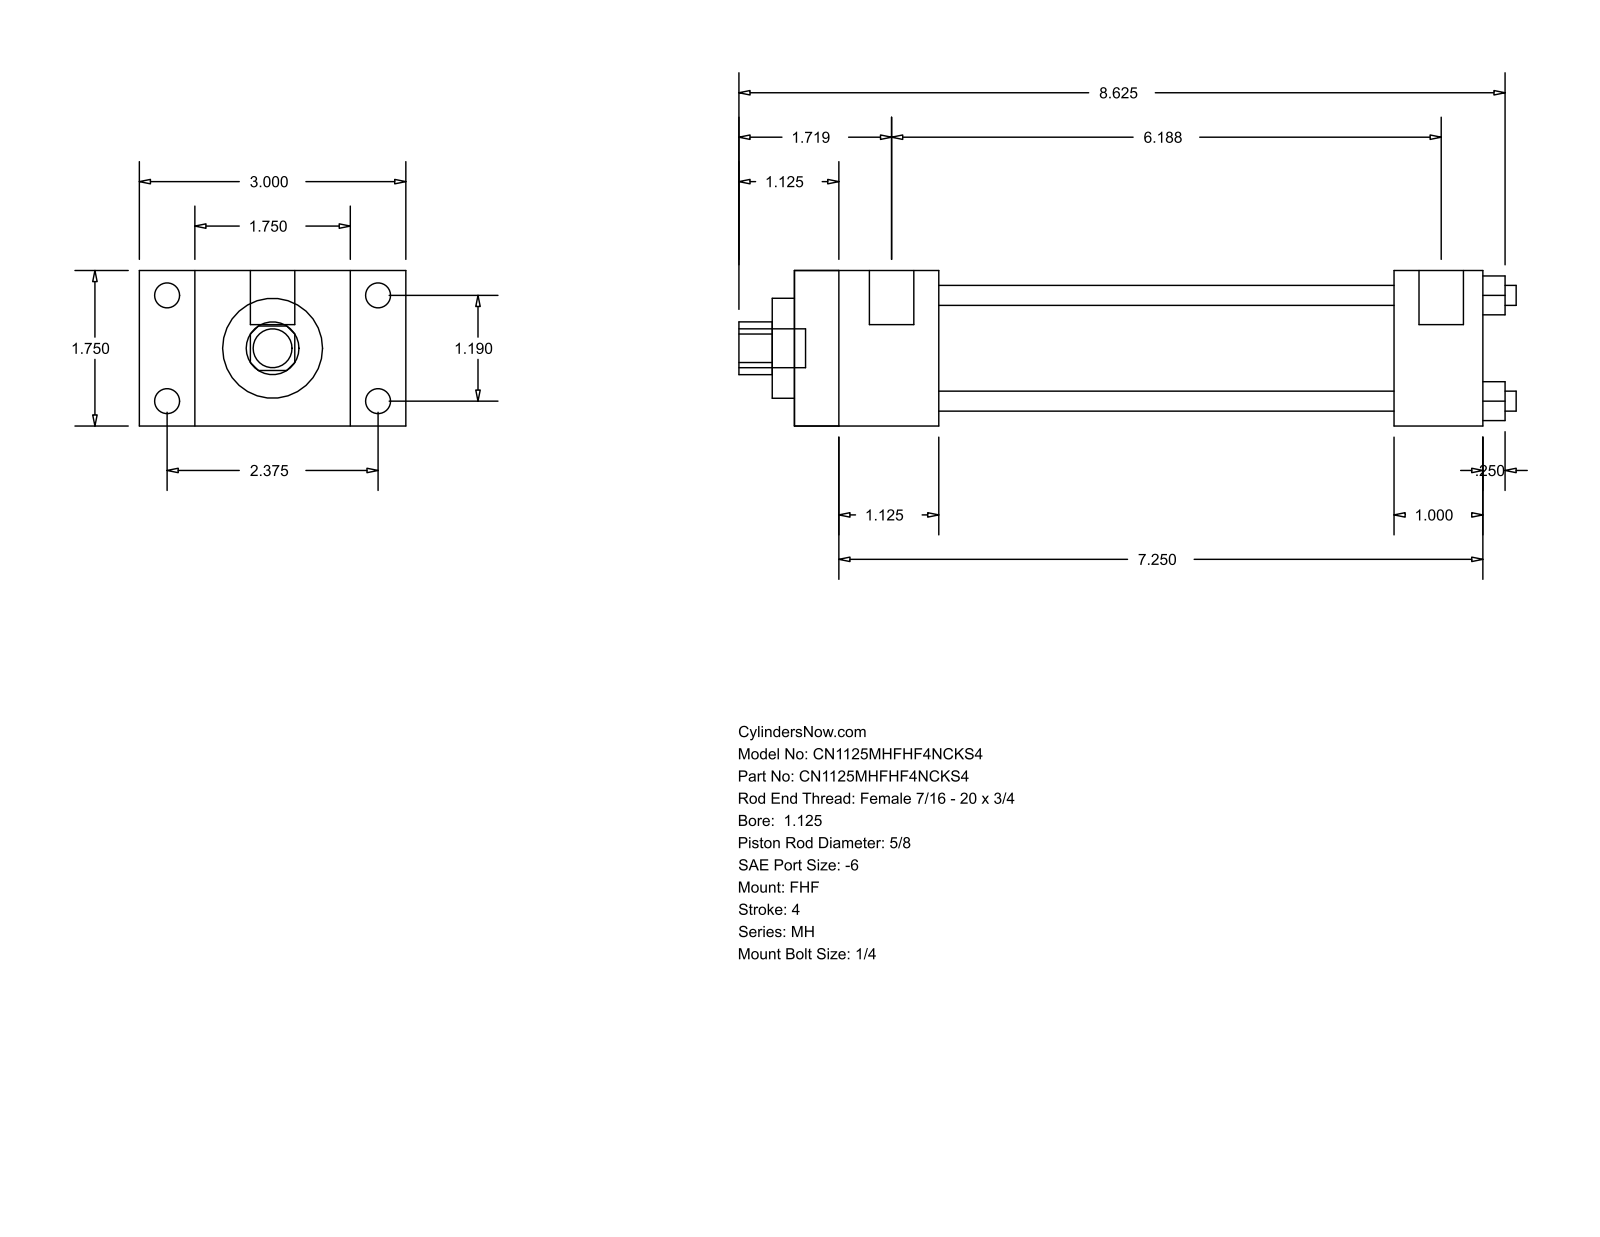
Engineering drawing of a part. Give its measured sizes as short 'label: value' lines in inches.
name: MH_FHF__0112_0.625
written by: GSSL Pune (CONFIG_CONTROL_DESIGN)
unit: in
bodies: 0 solids, 88 faces (60 planar, 28 cylindrical, 0 other)
size: 8.75 × 3 × 1.75
holes: 4× ⌀0.225, 1× ⌀0.625, 1× ⌀1.125, 1× ⌀1.375
bosses: 4× ⌀0.281, 4× ⌀0.219, 2× ⌀0.5, 1× ⌀0.437
rounds: 1× R0.297
face distances: 1.75, 0.625, 2.375, 1.625, 3, 7.75, 6.125, 6.75, 5.125, 1
hole spacings: 0.841, 1.19, 1.683
